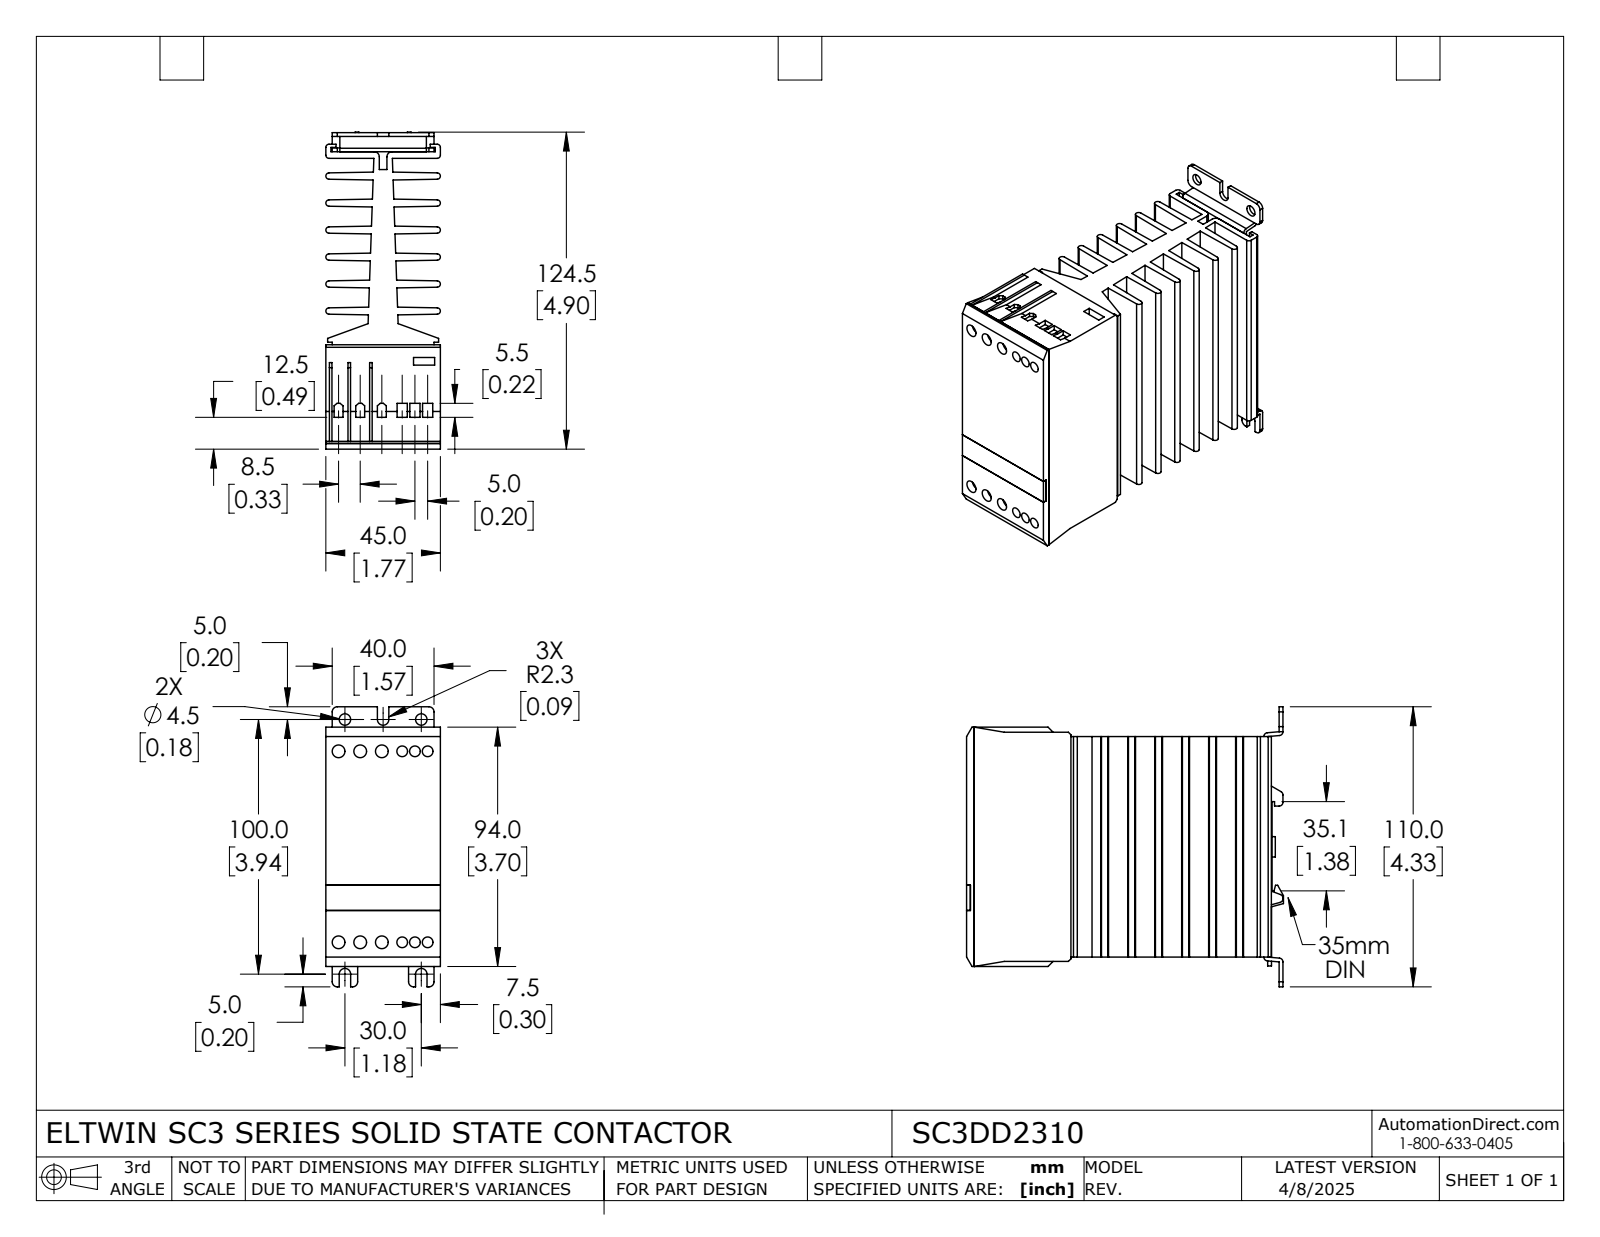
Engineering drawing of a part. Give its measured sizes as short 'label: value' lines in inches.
name: SC3DD2310
written by: SolidWorks 2021 (AUTOMOTIVE_DESIGN)
unit: in
bodies: 5 solids, 427 faces (316 planar, 111 cylindrical, 0 other)
size: 4.902 × 4.331 × 1.772
volume: 18.87 in³; area: 165.9 in²
holes: 6× ⌀0.165, 6× ⌀0.173, 6× ⌀0.197, 6× ⌀0.236, 2× ⌀0.177
bosses: 1× ⌀0.315
rounds: 18× R0.079, 16× R0.049, 10× R0.059, 4× R0.051, 3× R0.089
face distances: 0.417, 0.835, 0.127, 1.252, 0.29, 0.544, 0.707, 0.962, 1.669, 1.125
hole spacings: 2.953, 0.197, 0.335, 2.959, 2.972, 0.502, 1.181, 3.446
